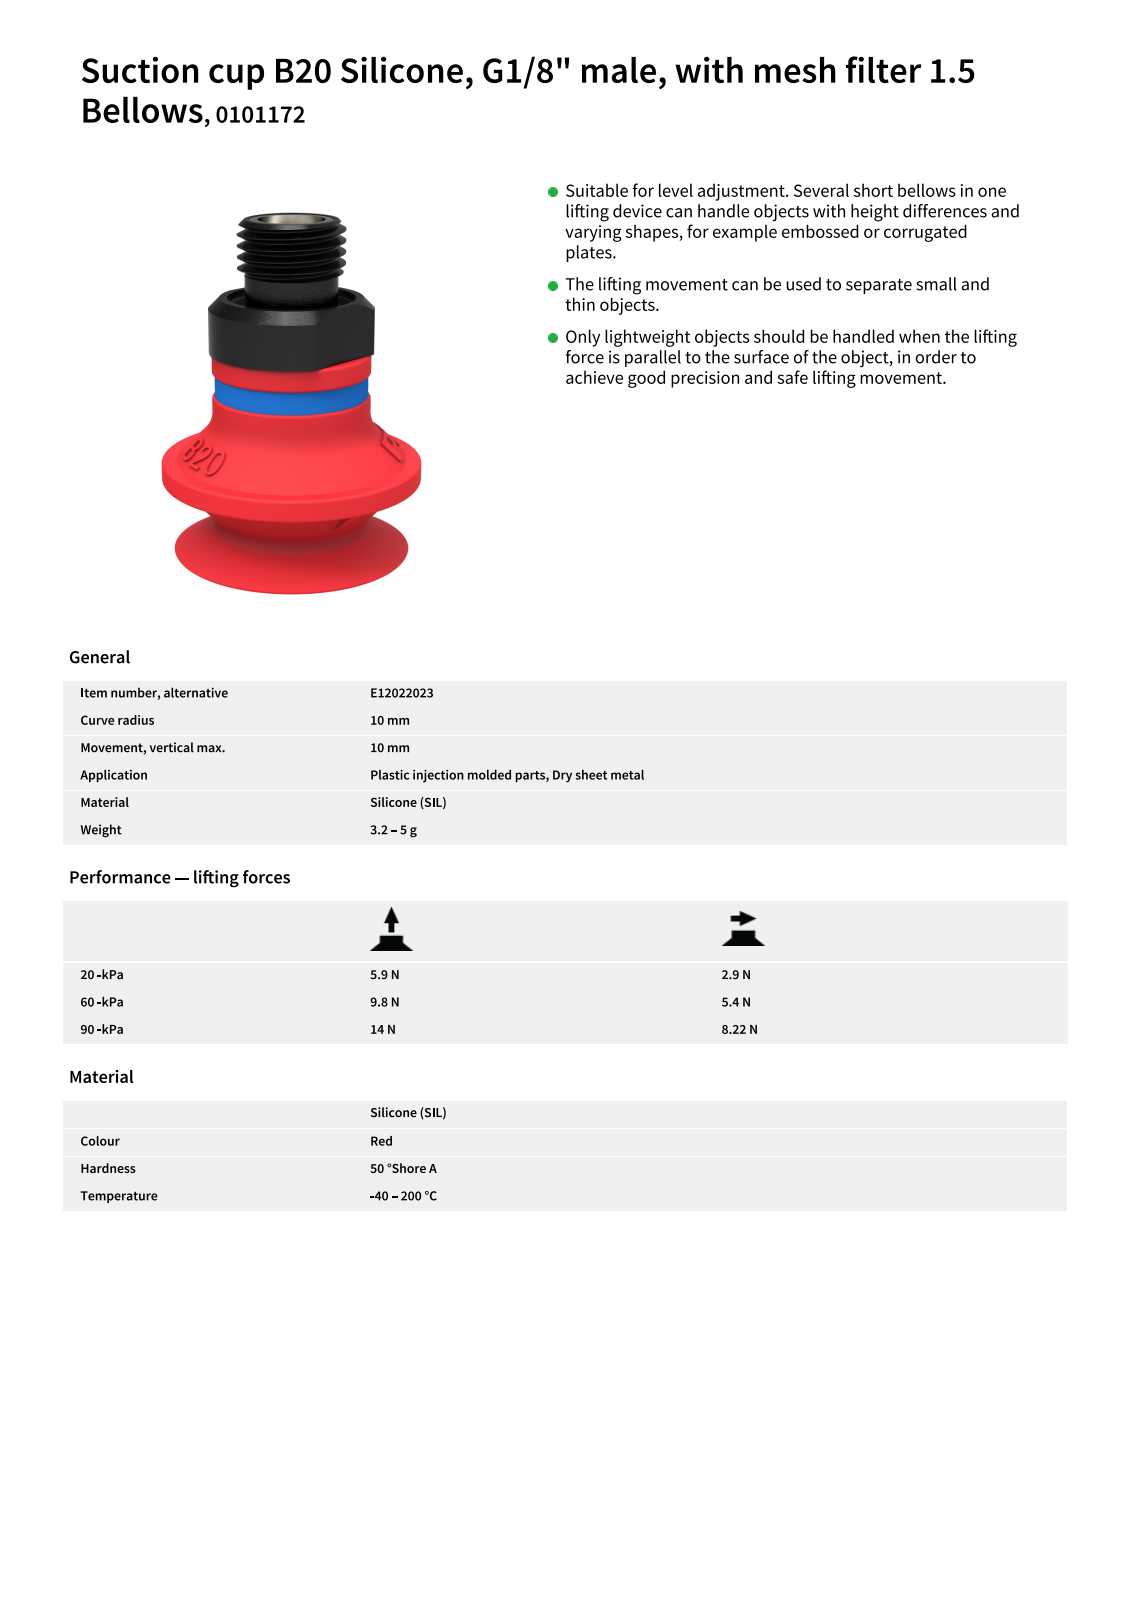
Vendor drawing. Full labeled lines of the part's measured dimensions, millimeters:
STEP written by: SolidEdge (CONFIG_CONTROL_DESIGN)
Units: millimetres
Bodies: 1 solid, 67 faces (29 planar, 15 cylindrical, 23 other)
Overall size (bounding box): 31 × 24 × 24
Volume: 3 140 mm³ · Surface area: 3 487 mm²
Round holes (diameter × count): ⌀4 ×1, ⌀5 ×1, ⌀11.5 ×1
Round bosses / shafts (diameter × count): ⌀24 ×1, ⌀14.5 ×1, ⌀14 ×1, ⌀9.73 ×1, ⌀8 ×1
Partial cylindrical surfaces — rounded edges, fillets, slot ends (radius × count): R2 ×4, R7.5 ×1
Main face-to-face distances: 7, 2, 24, 12, 9, 17, 31, 22, 19, 5
